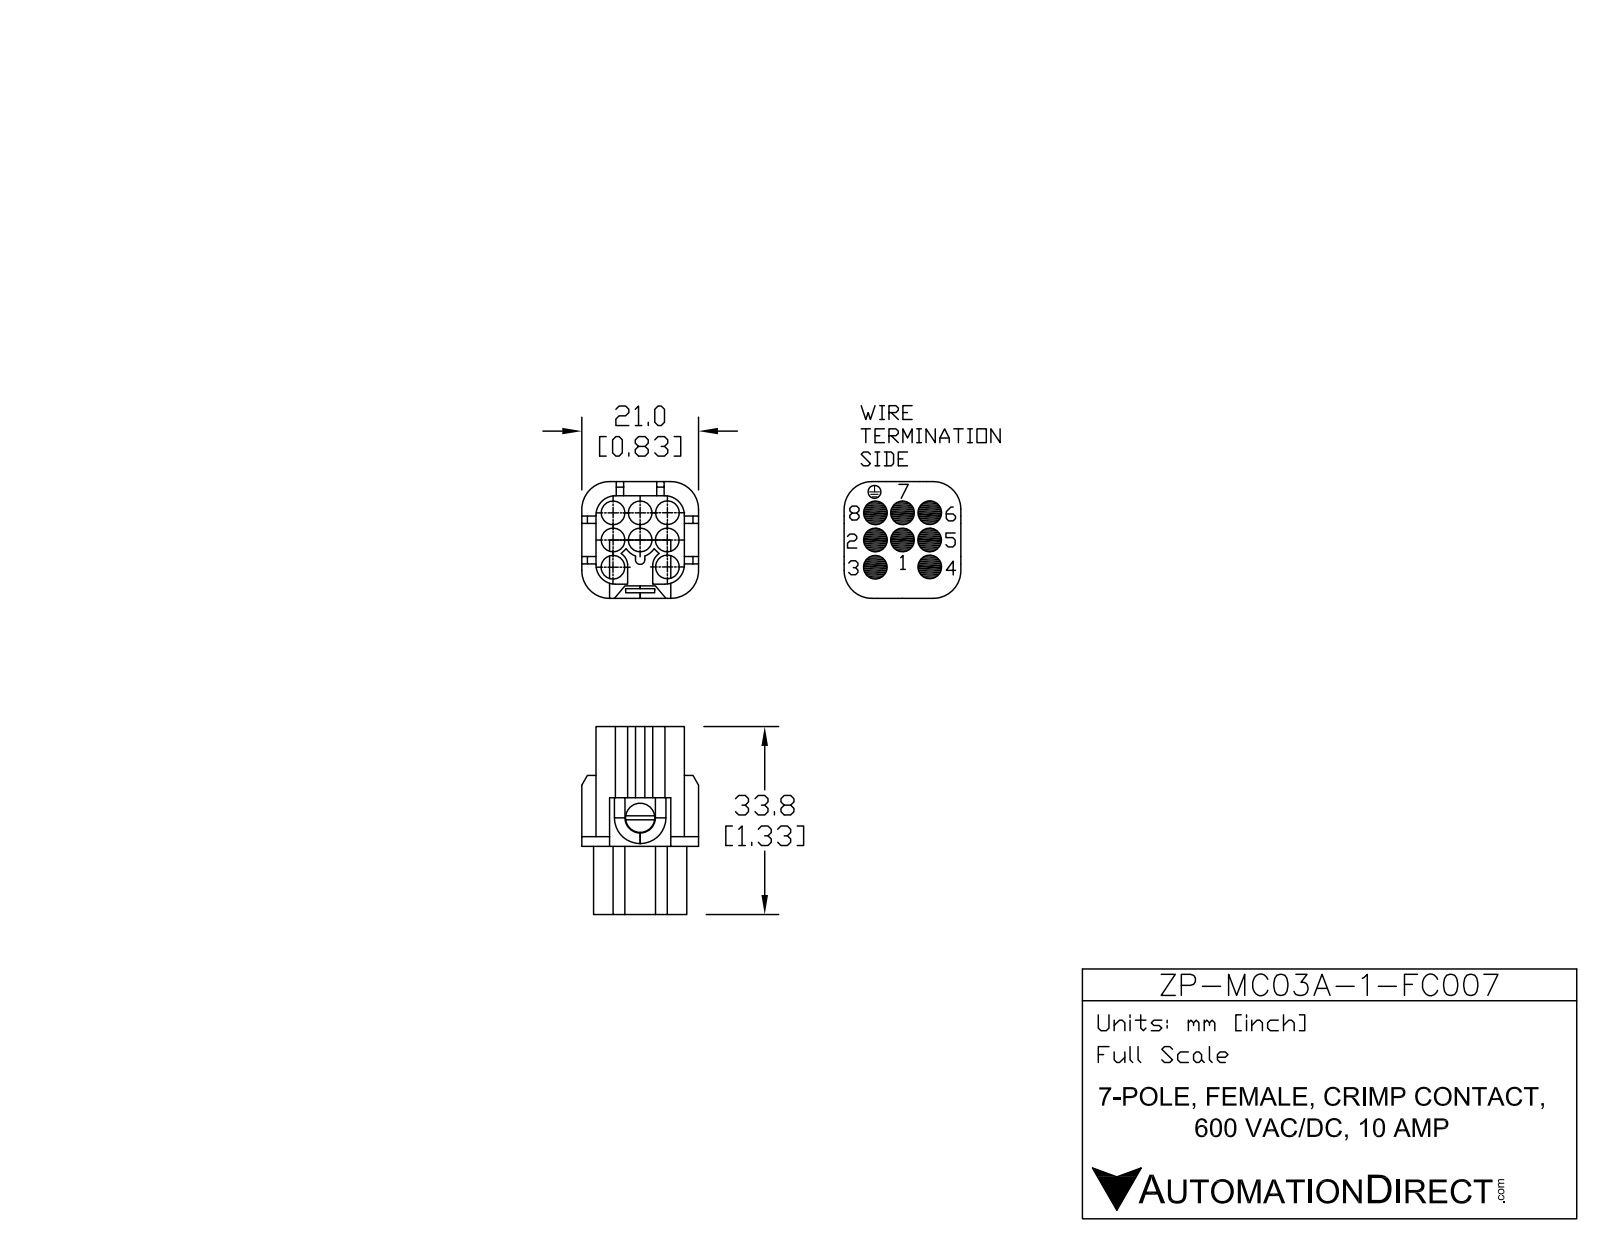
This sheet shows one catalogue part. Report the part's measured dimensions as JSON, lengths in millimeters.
{"part_name": "ZP-3A-7-FC-INSERT", "step_written_by": "SolidWorks 2011 (AUTOMOTIVE_DESIGN)", "units": "millimeters", "bodies": {"solids": 2, "faces": 134, "planar": 98, "cylindrical": 34, "other": 2}, "overall_size": [33.8, 21, 21], "volume_mm3": 5611, "surface_area_mm2": 6728, "round_holes": [[4.25, 8], [3.29, 4], [3.3, 4]], "round_bosses_or_shafts": [[5.25, 1]], "partial_cylinders_radius": [[3.5, 8], [5, 4], [2.65, 2], [3.54, 2], [0.84, 1]], "face_to_face_distances": [12.25, 16.33, 0.43, 8.25, 1.75, 15.9, 5, 7.75, 14, 5.2], "hole_center_spacings": [4.88, 4.9, 10.9, 4.87, 6.89, 9.78, 9.75, 9.76]}
